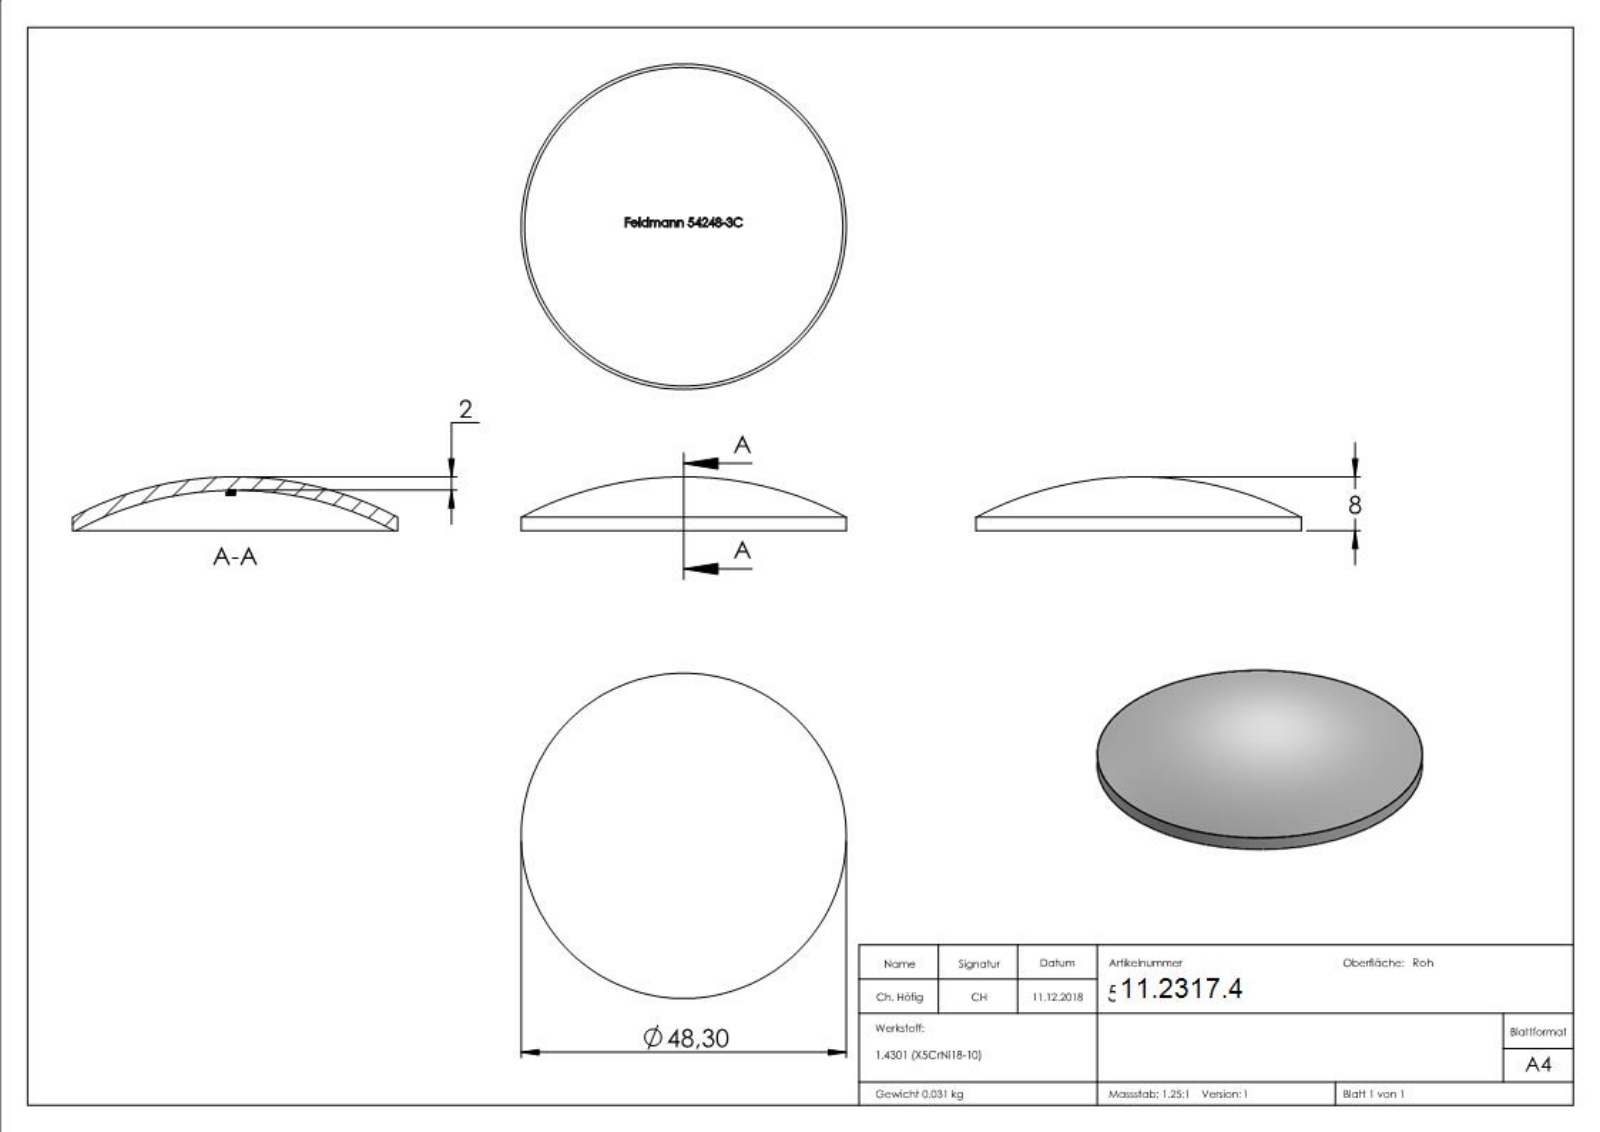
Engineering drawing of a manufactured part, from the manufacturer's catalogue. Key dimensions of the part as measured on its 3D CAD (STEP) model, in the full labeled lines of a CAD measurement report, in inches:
Part name (STEP PRODUCT): 54248-3C
STEP written by: SolidWorks 2015 (CONFIG_CONTROL_DESIGN)
Units: inches
Bodies: 1 solid, 246 faces (102 planar, 2 cylindrical, 142 other)
Overall size (bounding box): 1.902 × 1.902 × 0.315
Volume: 0.237 in³ · Surface area: 6.516 in²
Round bosses / shafts (diameter × count): ⌀1.902 ×1
Main face-to-face distances: 0.117, 0.015, 0.017, 0.08, 0.035, 0.049, 0.431, 0.351, 0.08, 0.065
